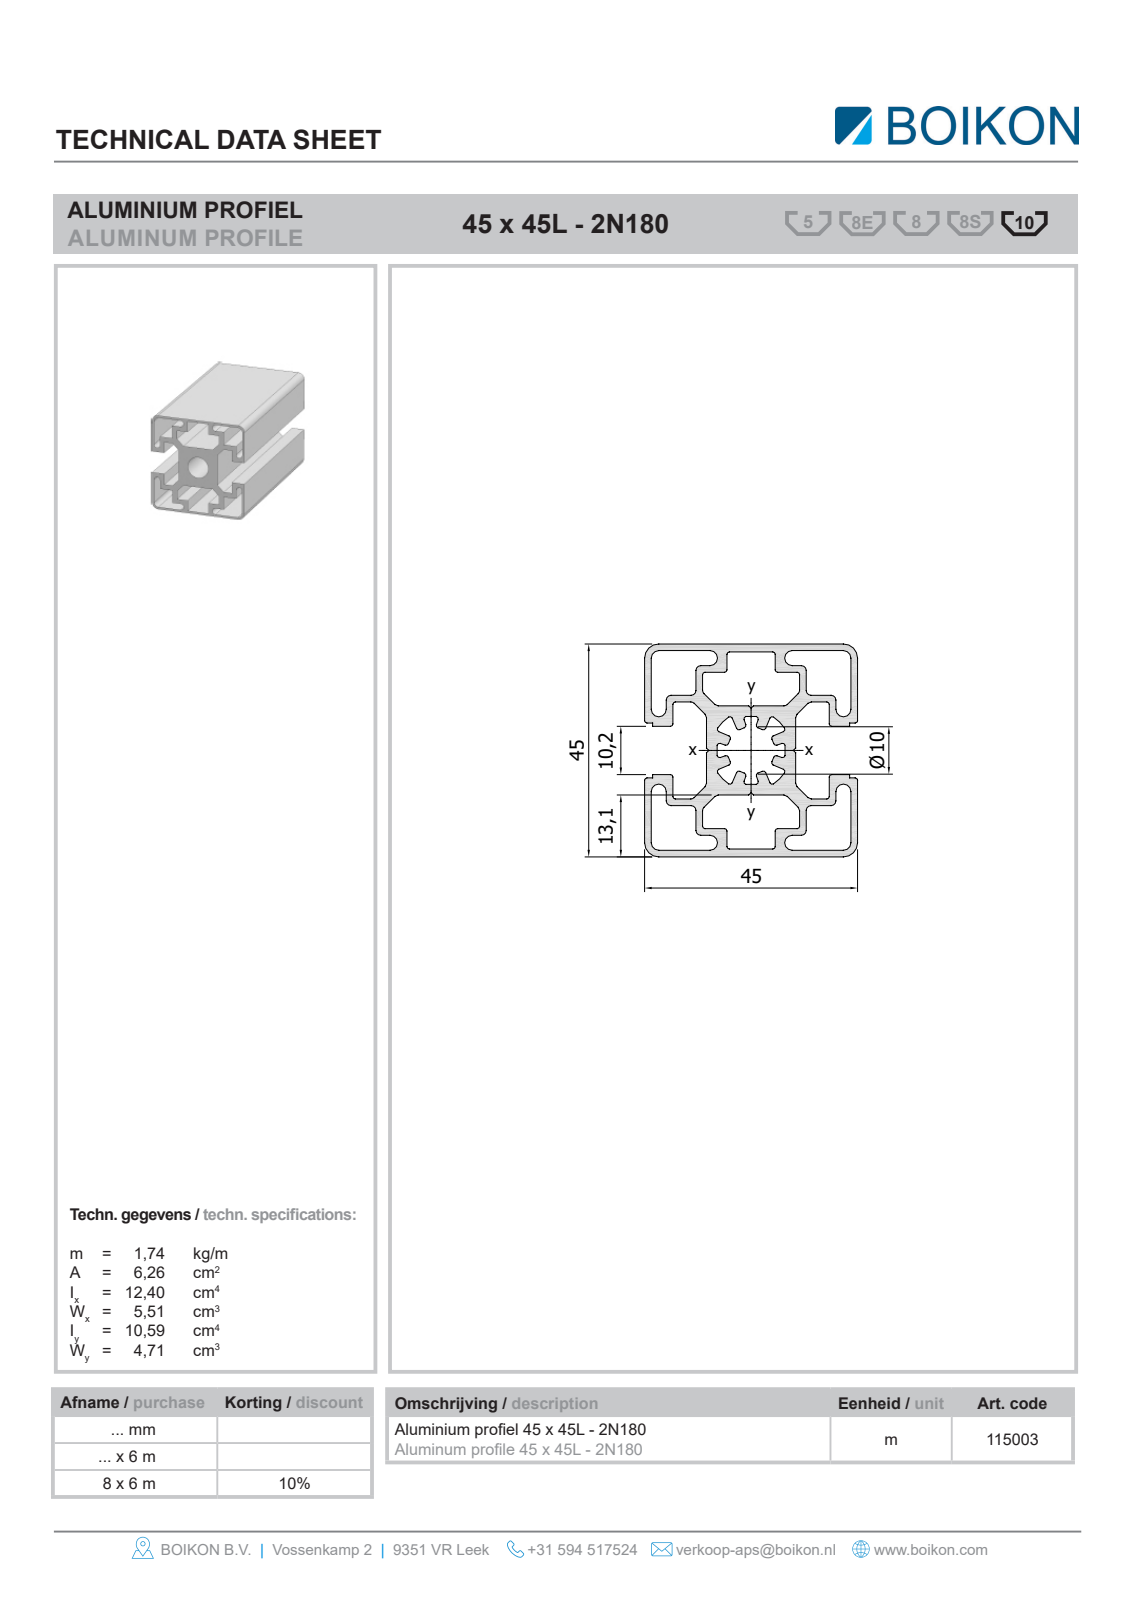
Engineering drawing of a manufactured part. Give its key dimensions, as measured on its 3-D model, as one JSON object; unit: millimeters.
{"part_name": "Root; 11500345x45L-2N180BOIKON0", "step_written_by": "HiCAD 2013 1802.4 Build 509 (AUTOMOTIVE_DESIGN)", "units": "millimeters", "bodies": {"solids": 1, "faces": 71, "planar": 62, "cylindrical": 9, "other": 0}, "overall_size": [1000, 45, 45], "volume_mm3": 850008, "surface_area_mm2": 558004, "round_holes": [[10, 1]], "partial_cylinders_radius": [[2, 4], [3, 4]], "face_to_face_distances": [1, 44, 10, 35, 45, 9, 34, 13.1, 3.1, 31.9]}
